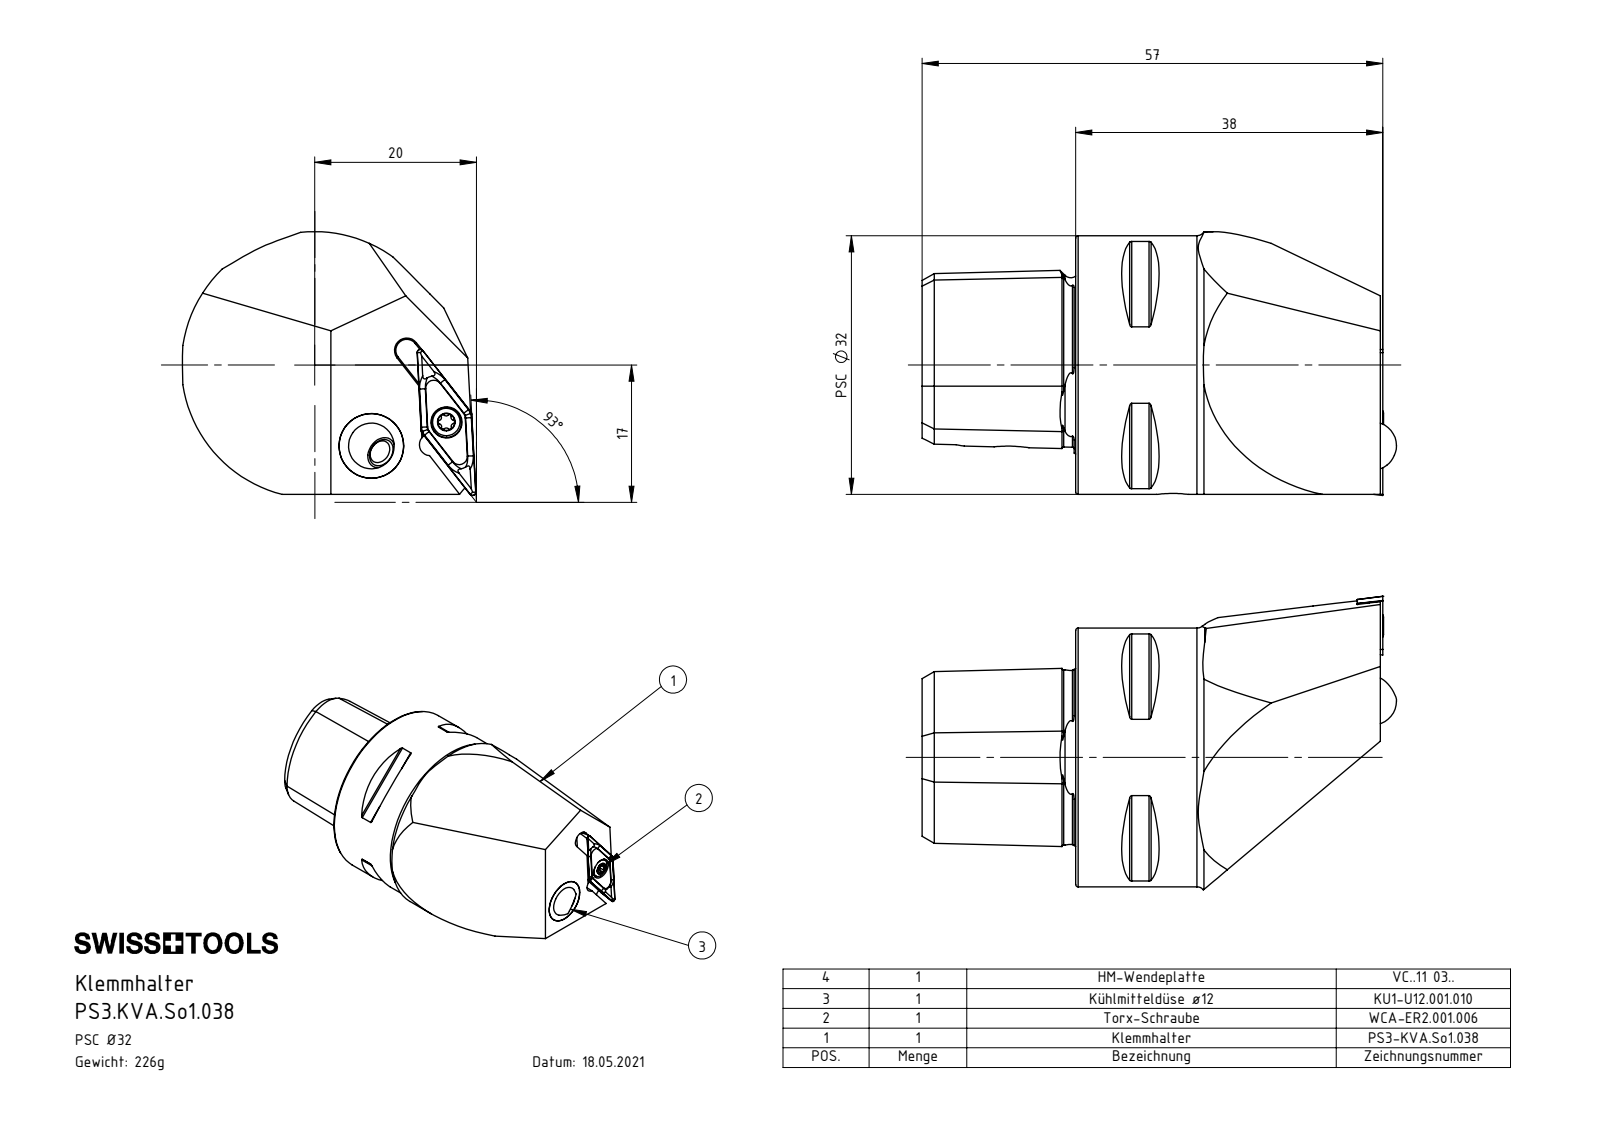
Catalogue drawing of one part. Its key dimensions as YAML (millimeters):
part_name: "VCGT110304; PS3.KVA.So1.038; KU1-U08.001.007_2; PS3-KVA.So1.038_A (+3 more)"
step_written_by: "SolidWorks 2017 (AUTOMOTIVE_DESIGN)"
units: millimeters
bodies: {solids: 5, faces: 258, planar: 57, cylindrical: 64, other: 137}
overall_size: [58.7, 36.31, 32.64]
volume: 28812
surface_area: 8945
round_holes:
  - {diameter: 2.05, count: 1}
  - {diameter: 2.8, count: 1}
  - {diameter: 2.9, count: 1}
  - {diameter: 3.6, count: 1}
  - {diameter: 3.85, count: 1}
  - {diameter: 4, count: 1}
  - {diameter: 4.2, count: 1}
  - {diameter: 5, count: 1}
  - {diameter: 8, count: 1}
  - {diameter: 10.2, count: 1}
  - {diameter: 15, count: 1}
  - {diameter: 16.5, count: 1}
round_bosses_or_shafts:
  - {diameter: 32, count: 1}
  - {diameter: 3.4, count: 1}
  - {diameter: 2.5, count: 1}
partial_cylinders:
  - {radius: 0.3, count: 8}
  - {radius: 0.21, count: 6}
  - {radius: 0.36, count: 5}
  - {radius: 1.35, count: 2}
  - {radius: 0.36, count: 1}
  - {radius: 3, count: 1}
  - {radius: 16.5, count: 1}
  - {radius: 24, count: 1}
face_to_face_distances: [37.7, 34.82, 2.88, 19, 53.82, 56.7, 12.01, 50.4, 31.4, 3.42]
hole_center_spacings: [9.73, 9.74, 12.21, 17.73, 17.78, 20]
